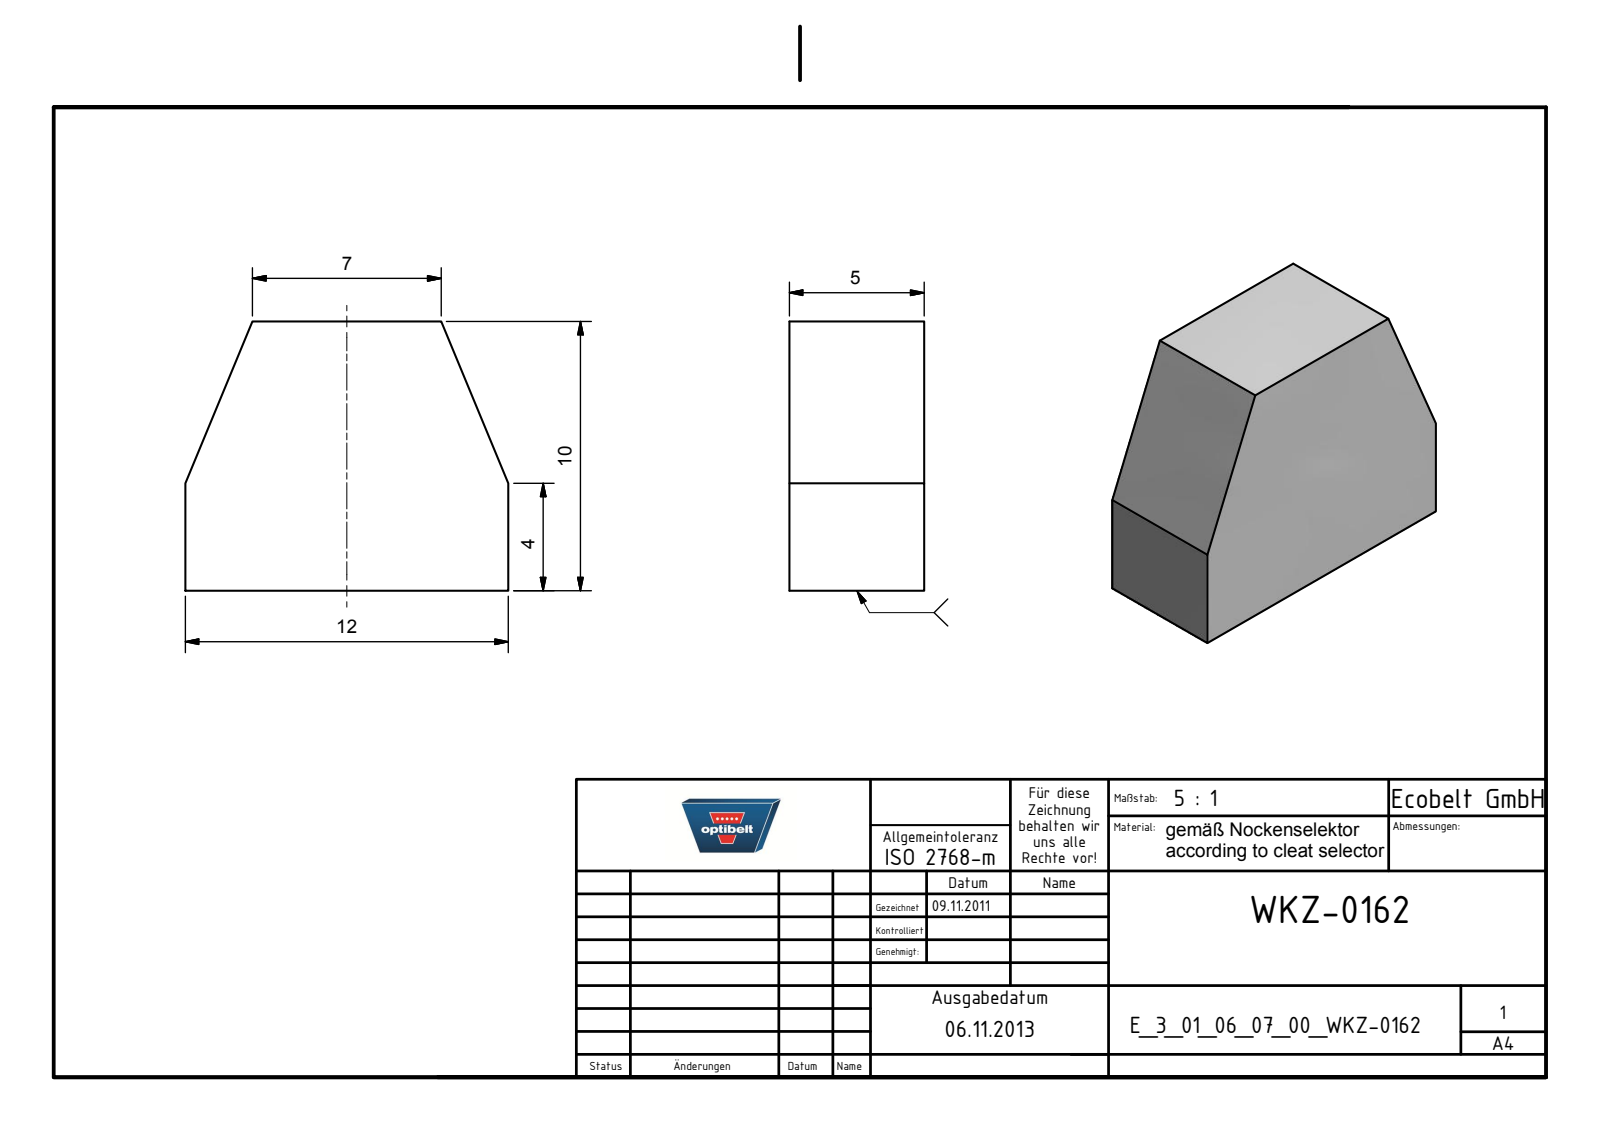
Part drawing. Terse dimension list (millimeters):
name: E_3_01_06_07_00_WKZ-0162
written by: Autodesk Inventor 2025 (AUTOMOTIVE_DESIGN)
unit: mm
bodies: 1 solid, 8 faces (8 planar, 0 cylindrical, 0 other)
size: 12 × 10 × 5
volume: 525 mm³; area: 410 mm²
face distances: 5, 10, 12
